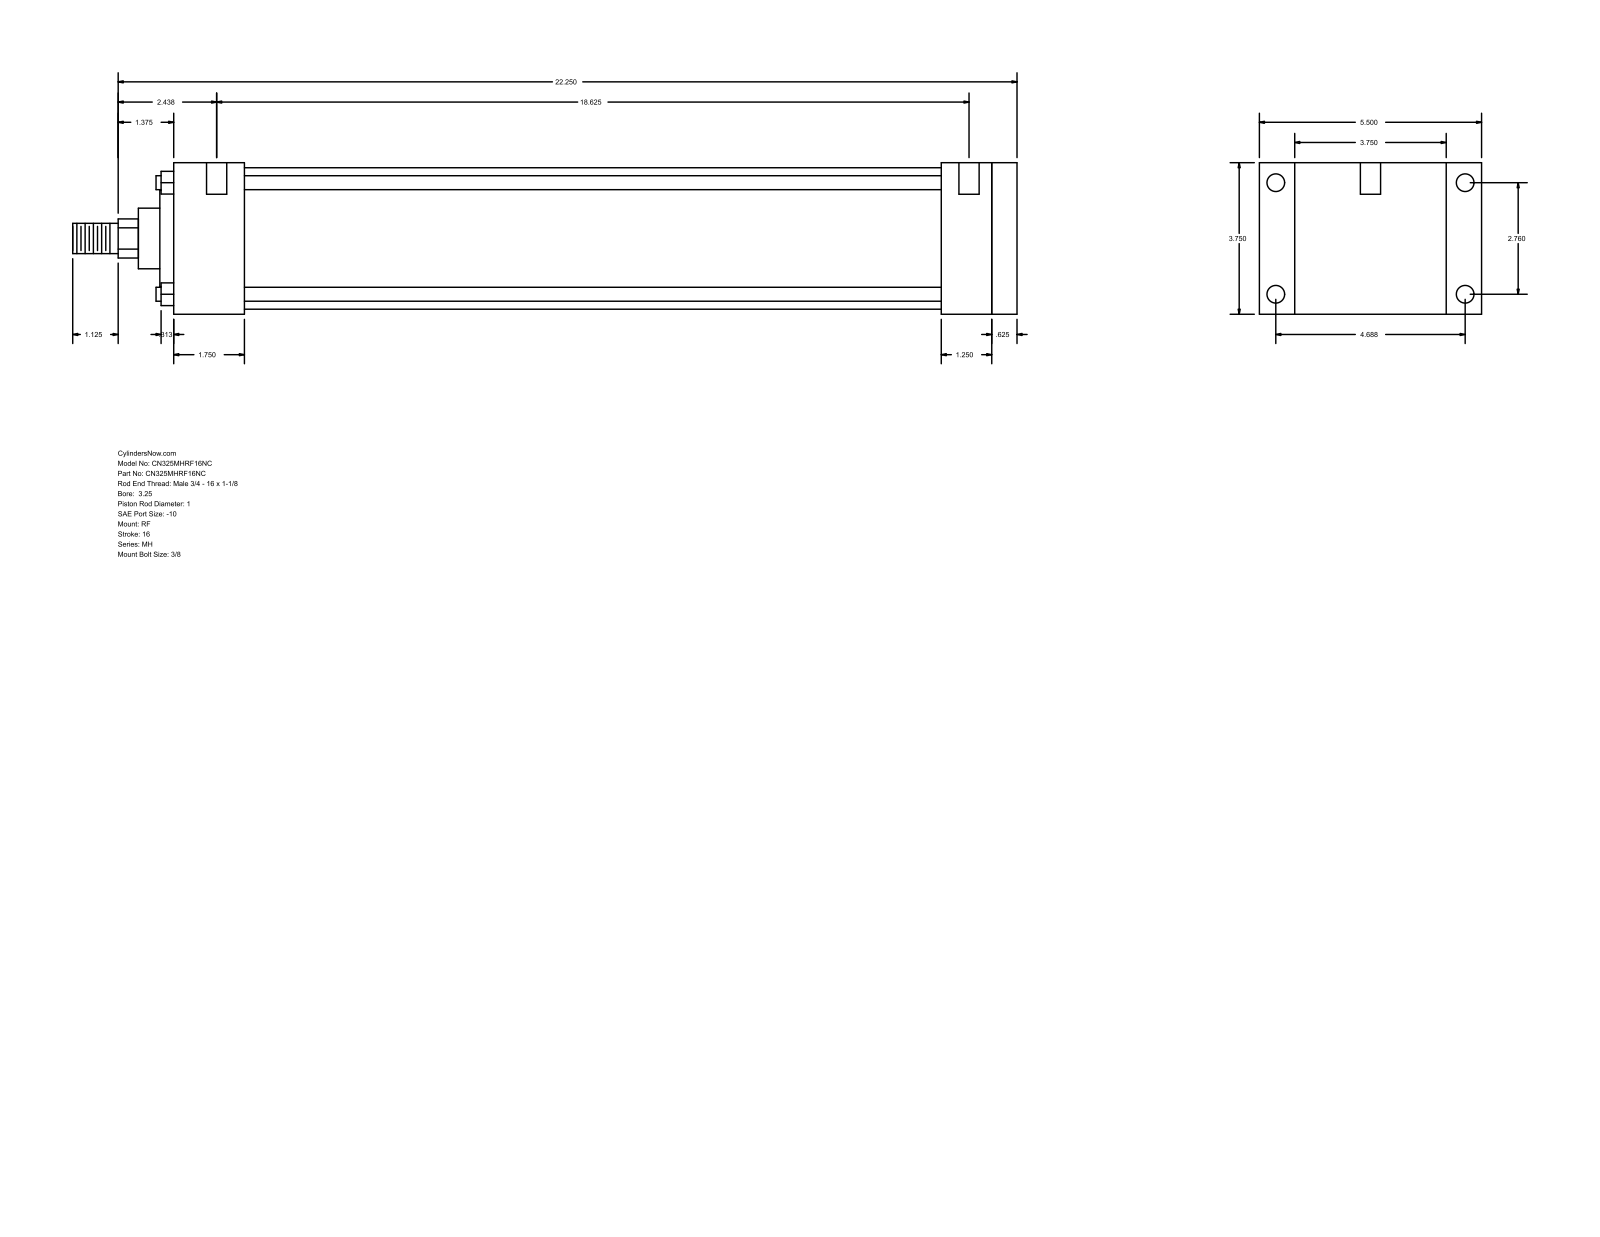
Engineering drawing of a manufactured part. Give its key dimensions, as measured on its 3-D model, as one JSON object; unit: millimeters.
{"part_name": "MH_RF__0325_1", "step_written_by": "GSSL Pune (CONFIG_CONTROL_DESIGN)", "units": "millimeters", "bodies": {"solids": 0, "faces": 94, "planar": 65, "cylindrical": 29, "other": 0}, "overall_size": [593.73, 139.7, 95.25], "round_holes": [[5.56, 4], [11.13, 4], [12.7, 2]], "round_bosses_or_shafts": [[8.76, 4], [88.9, 1], [60.33, 1], [38.1, 1], [25.4, 1], [19.05, 1]], "partial_cylinders_radius": [[12.29, 1]], "face_to_face_distances": [95.24, 530.23, 514.35, 15.88, 22.23, 117.47, 44.46, 469.89, 485.77, 482.6], "hole_center_spacings": [70.1, 119.06, 138.16, 479.42, 1.58, 4.76, 473.08, 474.66]}
